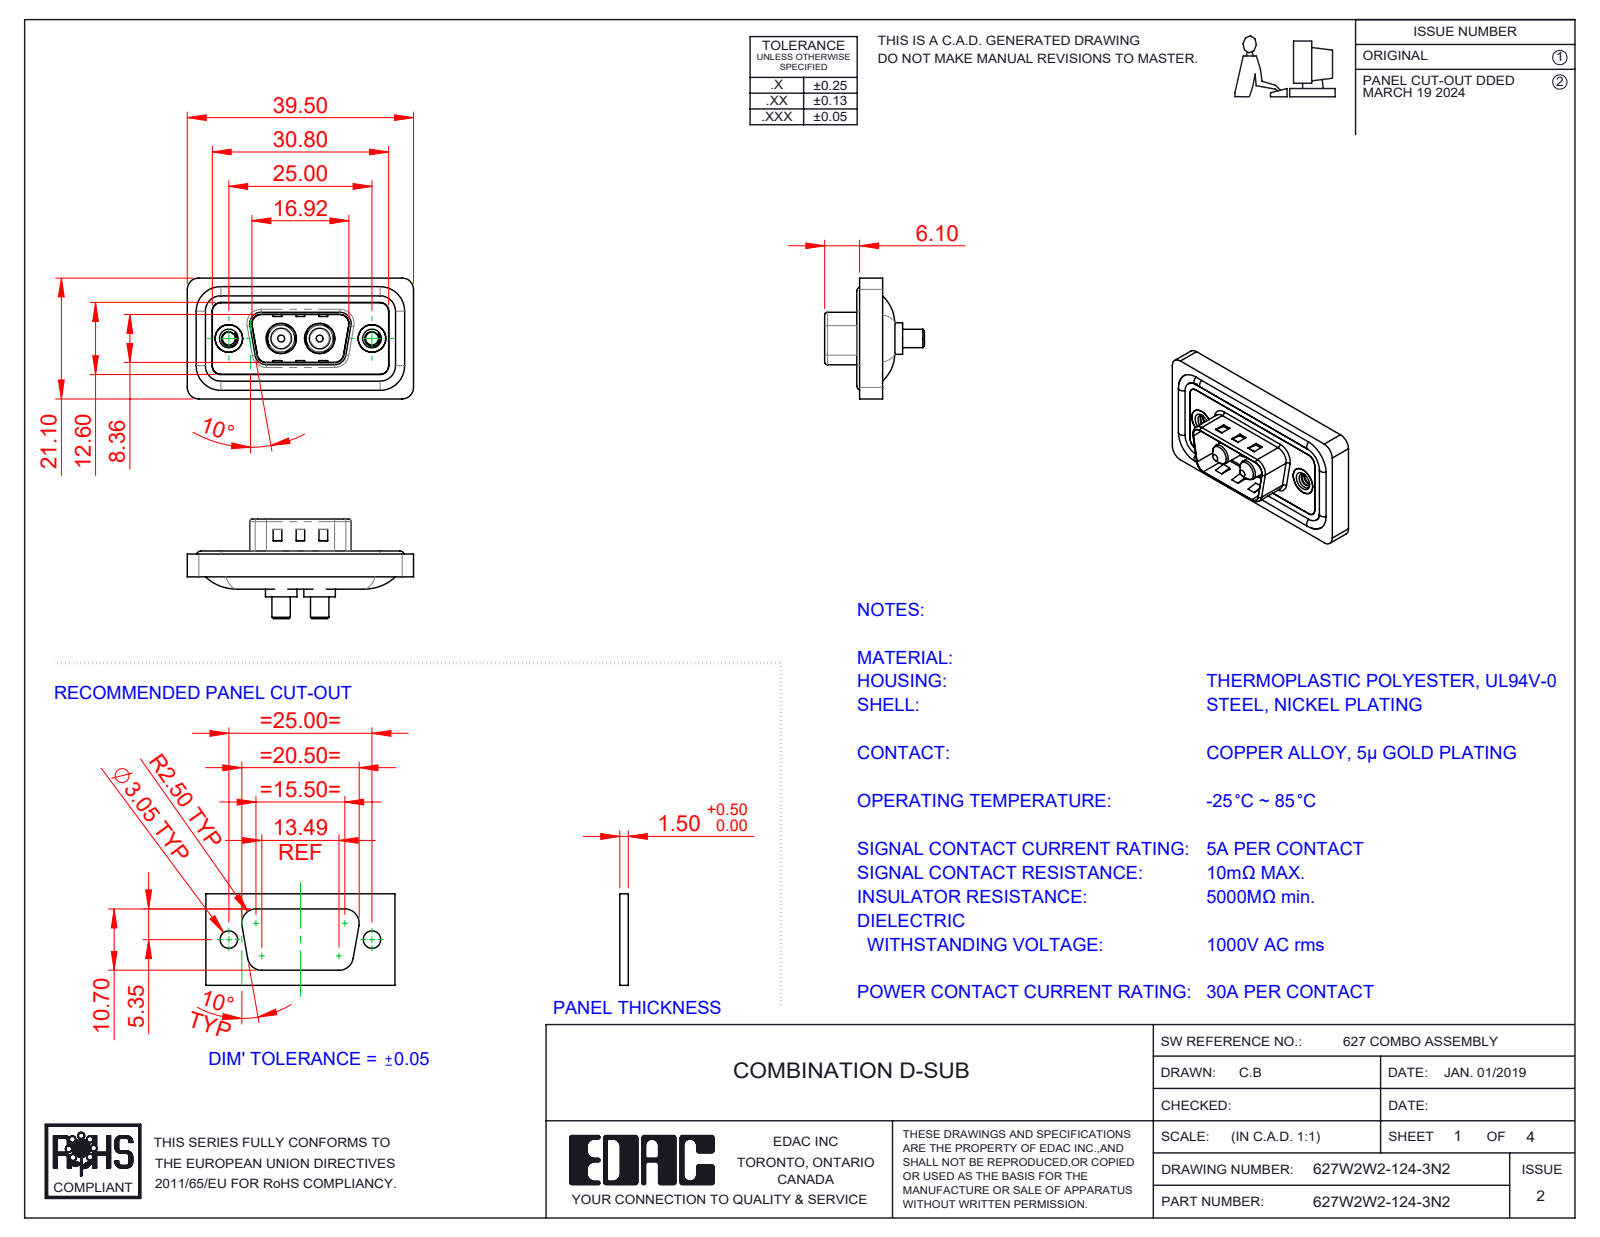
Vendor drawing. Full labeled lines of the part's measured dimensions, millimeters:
Part name (STEP PRODUCT): 627Combo Housing_2W2; 627Combo Waterproof Housing_09 Contacts; Power Pin_30A S; 627Combo Shell Front_09 Contacts (+3 more)
STEP written by: SolidWorks 2023 (CONFIG_CONTROL_DESIGN)
Units: millimetres
Bodies: 11 solids, 489 faces (165 planar, 218 cylindrical, 106 other)
Overall size (bounding box): 39.5 × 21.1 × 17.4
Volume: 4 475 mm³ · Surface area: 6 993 mm²
Round holes (diameter × count): ⌀2.26 ×2, ⌀4 ×2, ⌀4.8 ×2, ⌀4.85 ×2, ⌀5 ×2, ⌀5.3 ×2
Round bosses / shafts (diameter × count): ⌀1.6 ×4, ⌀5.5 ×2, ⌀5.2 ×2, ⌀4.9 ×2, ⌀4.75 ×2, ⌀3.75 ×2, ⌀3.6 ×2, ⌀3.2 ×2
Partial cylindrical surfaces — rounded edges, fillets, slot ends (radius × count): R1.5 ×22, R2 ×18, R0.5 ×8, R1.6 ×8, R0.25 ×4, R0.6 ×4, R0.65 ×4, R0.9 ×4
Main face-to-face distances: 0.4, 1.1, 2.9, 3.1, 0.5, 1.6, 1.5, 4, 2.5, 0.7
Hole centre spacings: 9.14, 15.86, 6.72, 25
